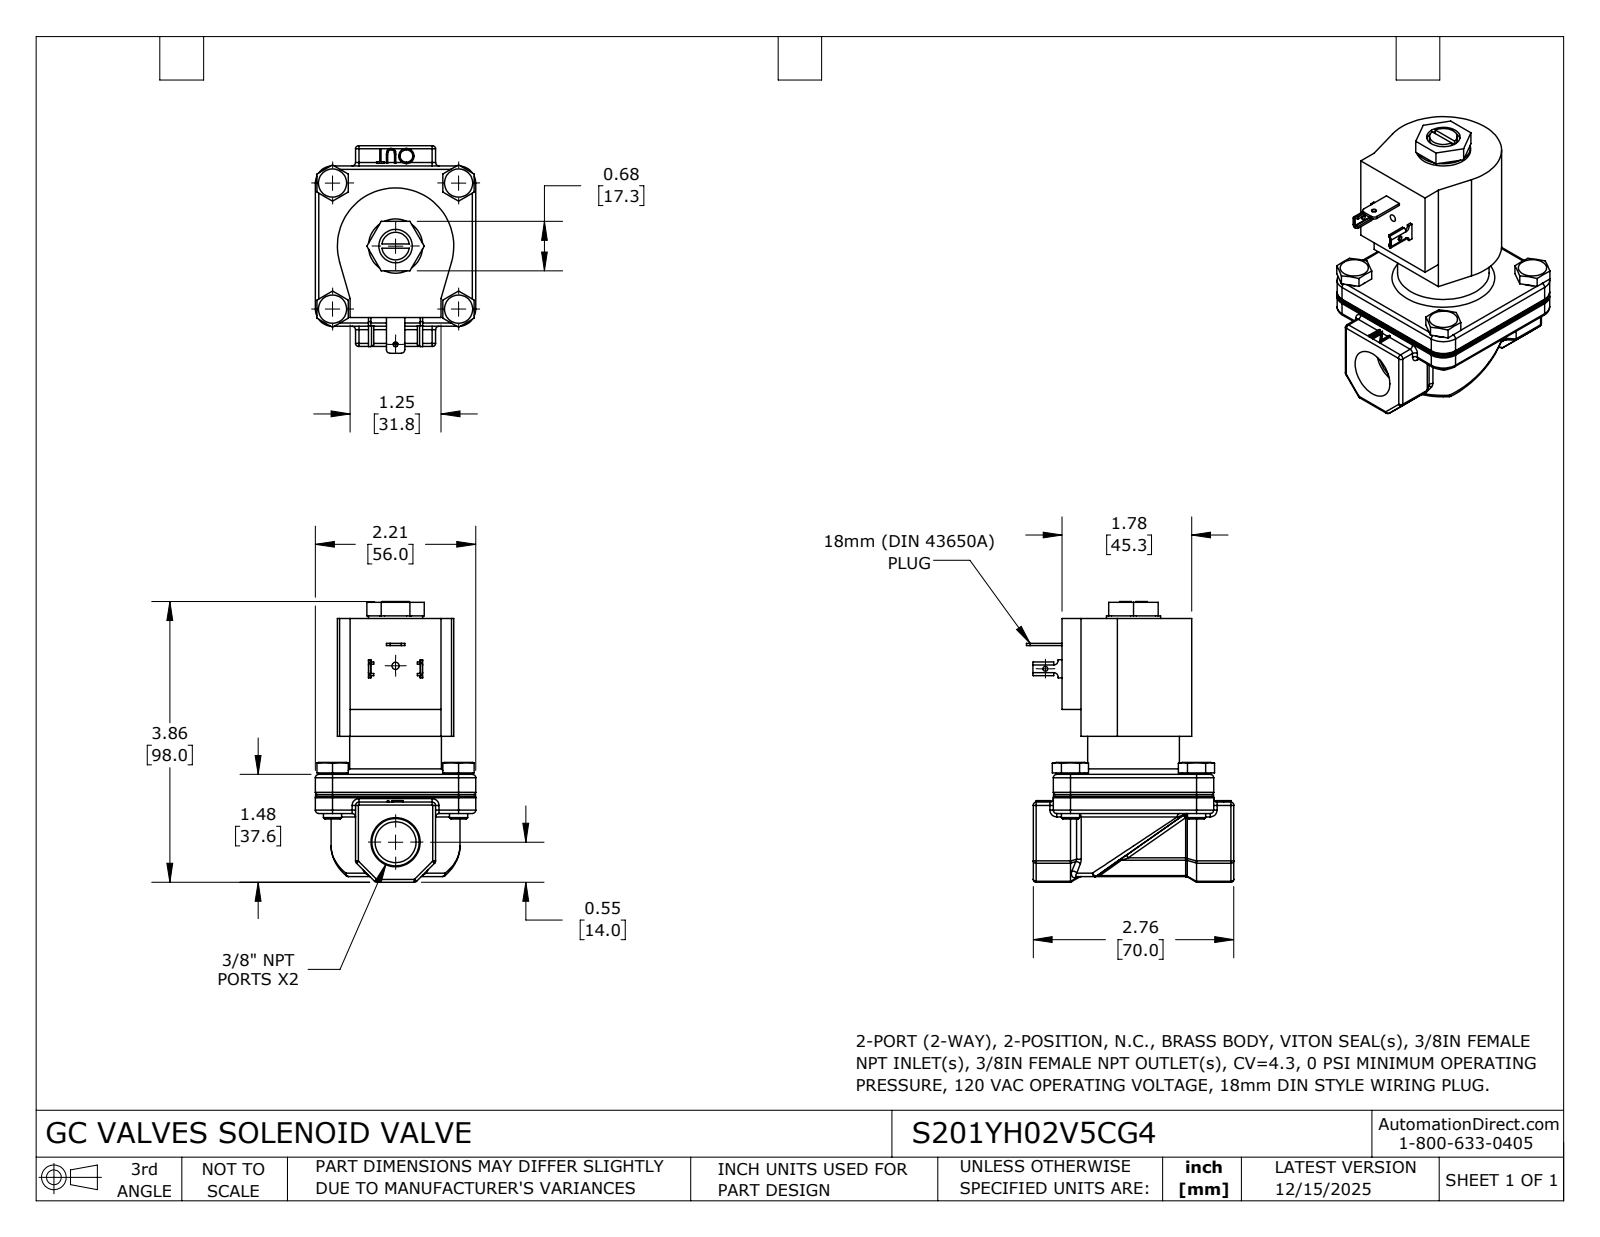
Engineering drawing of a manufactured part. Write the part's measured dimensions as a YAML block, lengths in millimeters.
part_name: "S201YH02V5CG4"
step_written_by: "SolidWorks 2024 (CONFIG_CONTROL_DESIGN)"
units: millimeters
bodies: {solids: 1, faces: 483, planar: 204, cylindrical: 153, other: 126}
overall_size: [98, 72.4, 56]
volume: 159000
surface_area: 26080
round_holes:
  - {diameter: 1.7, count: 1}
  - {diameter: 1.7, count: 1}
  - {diameter: 2.5, count: 1}
  - {diameter: 11.7, count: 1}
  - {diameter: 14.3, count: 1}
round_bosses_or_shafts:
  - {diameter: 9.9, count: 4}
  - {diameter: 6.4, count: 4}
  - {diameter: 32, count: 1}
  - {diameter: 18.9, count: 1}
  - {diameter: 9.7, count: 1}
partial_cylinders:
  - {radius: 1.2, count: 57}
  - {radius: 1, count: 12}
  - {radius: 0.2, count: 4}
  - {radius: 0.8, count: 4}
  - {radius: 1, count: 4}
  - {radius: 5.9, count: 4}
  - {radius: 6, count: 4}
  - {radius: 1.3, count: 2}
face_to_face_distances: [54.4, 14, 42, 56, 13.6, 68.1, 7, 63, 26.9, 13.3]
hole_center_spacings: [34.3, 61.5]
